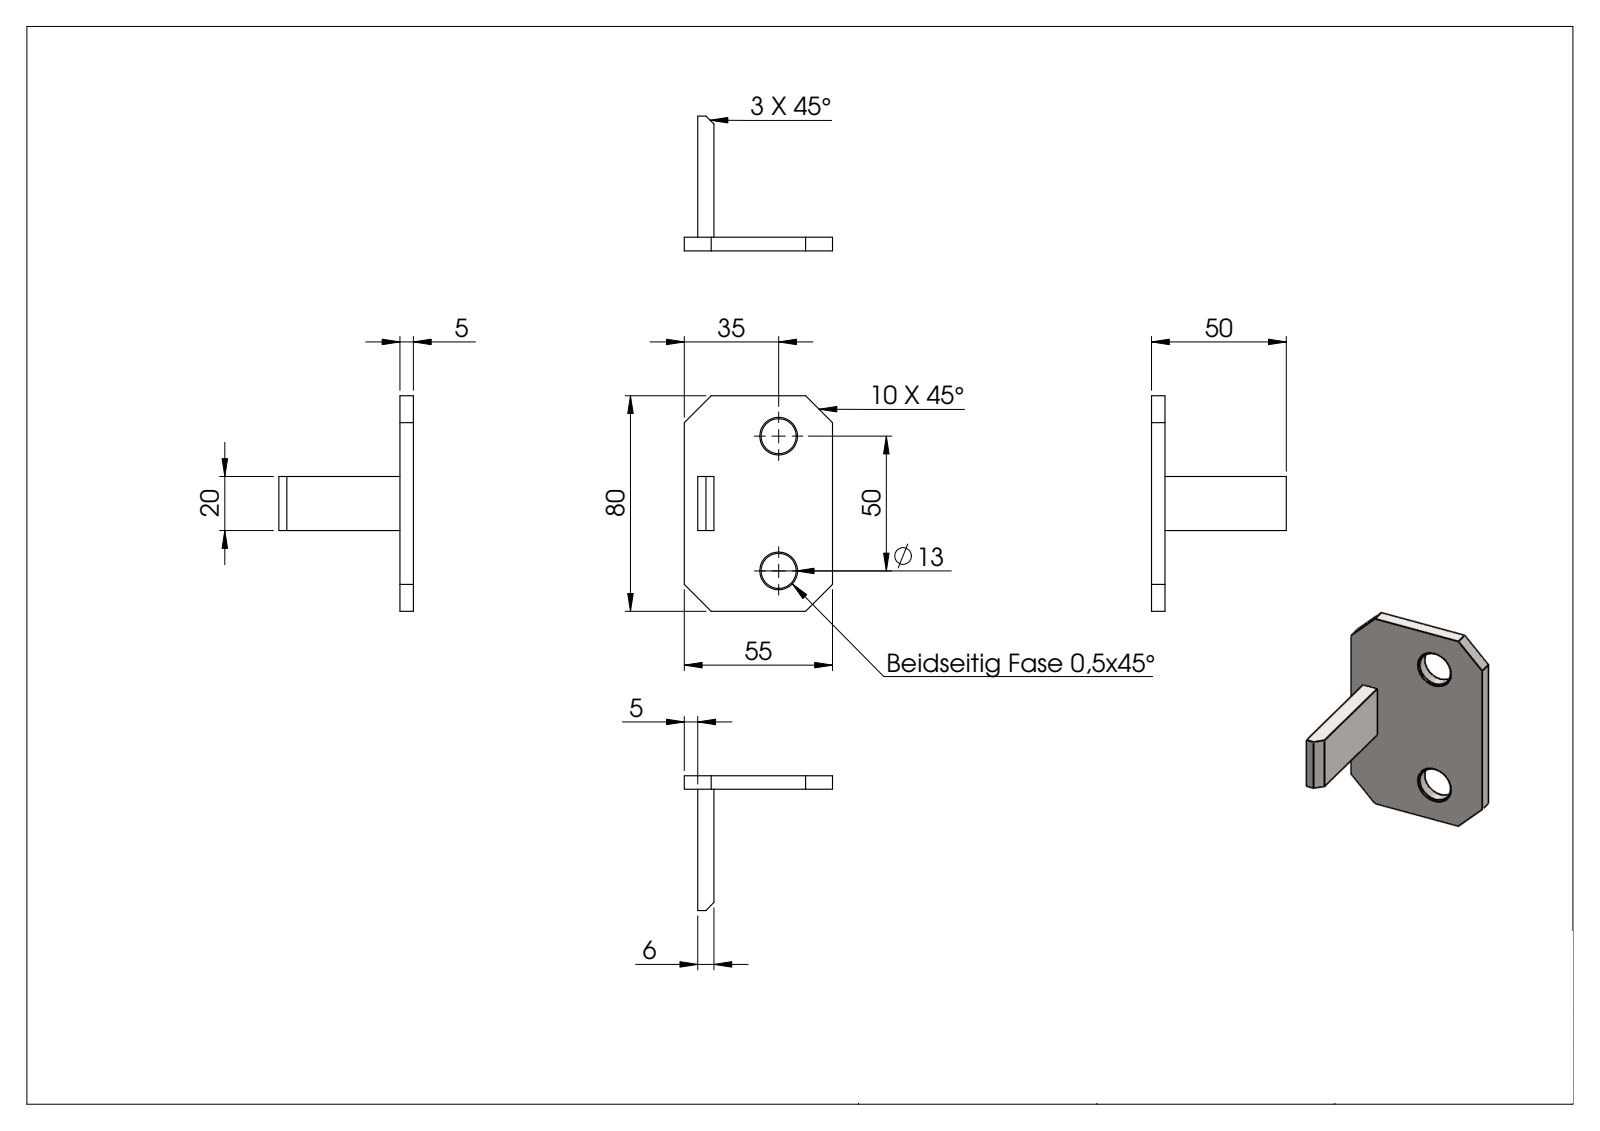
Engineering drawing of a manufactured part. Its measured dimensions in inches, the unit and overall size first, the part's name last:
Units: inches
Overall size (bounding box): 3.15 × 2.165 × 1.969
Round holes (diameter × count): ⌀0.512 ×2
Main face-to-face distances: 0.197, 0.236, 1.969, 1.181, 0.433, 2.165, 1.732, 0.787, 3.15, 3.201
Hole centre spacings: 1.969
Volume: 1.523 in³ · Surface area: 18.24 in²
Bodies: 1 solid, 197 faces (111 planar, 4 cylindrical, 82 other)
Part name (STEP PRODUCT): 1648
STEP written by: SolidWorks 2015 (CONFIG_CONTROL_DESIGN)
